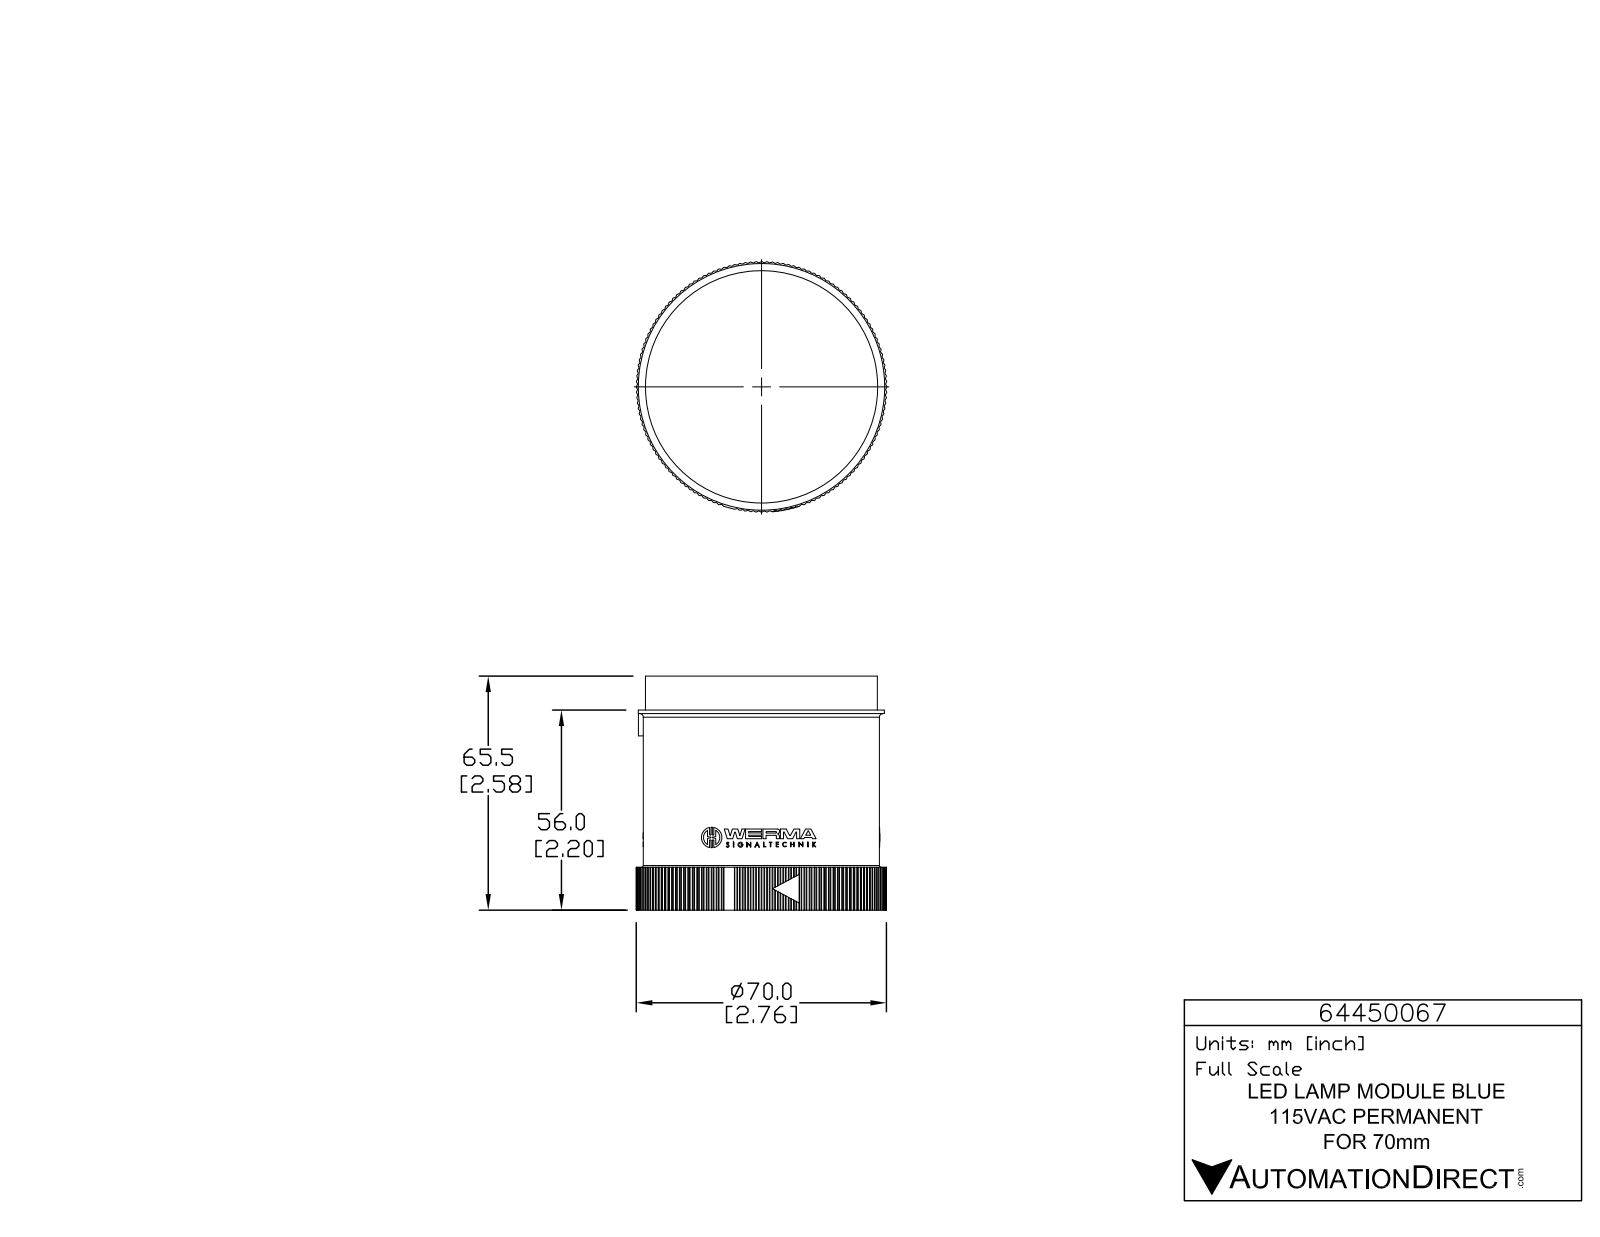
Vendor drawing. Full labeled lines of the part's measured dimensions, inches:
Part name (STEP PRODUCT): 64450067
STEP written by: SolidWorks 2015 (AUTOMOTIVE_DESIGN)
Units: inches
Bodies: 1 solid, 1400 faces (832 planar, 563 cylindrical, 5 other)
Overall size (bounding box): 2.762 × 2.762 × 2.579
Volume: 12.02 in³ · Surface area: 37.48 in²
Round holes (diameter × count): ⌀0.039 ×3, ⌀2.575 ×1
Round bosses / shafts (diameter × count): ⌀0.226 ×3, ⌀0.056 ×3, ⌀2.717 ×1, ⌀2.606 ×1, ⌀2.559 ×1
Partial cylindrical surfaces — rounded edges, fillets, slot ends (radius × count): R0.008 ×285, R0.008 ×6, R0.008 ×6, R0.008 ×6, R0.131 ×6, R0.004 ×3, R0.005 ×3, R0.008 ×3
Main face-to-face distances: 2.201, 2.451, 0.378, 2.579, 2.205, 1.827, 0.374, 2.452, 0.472, 0.094
